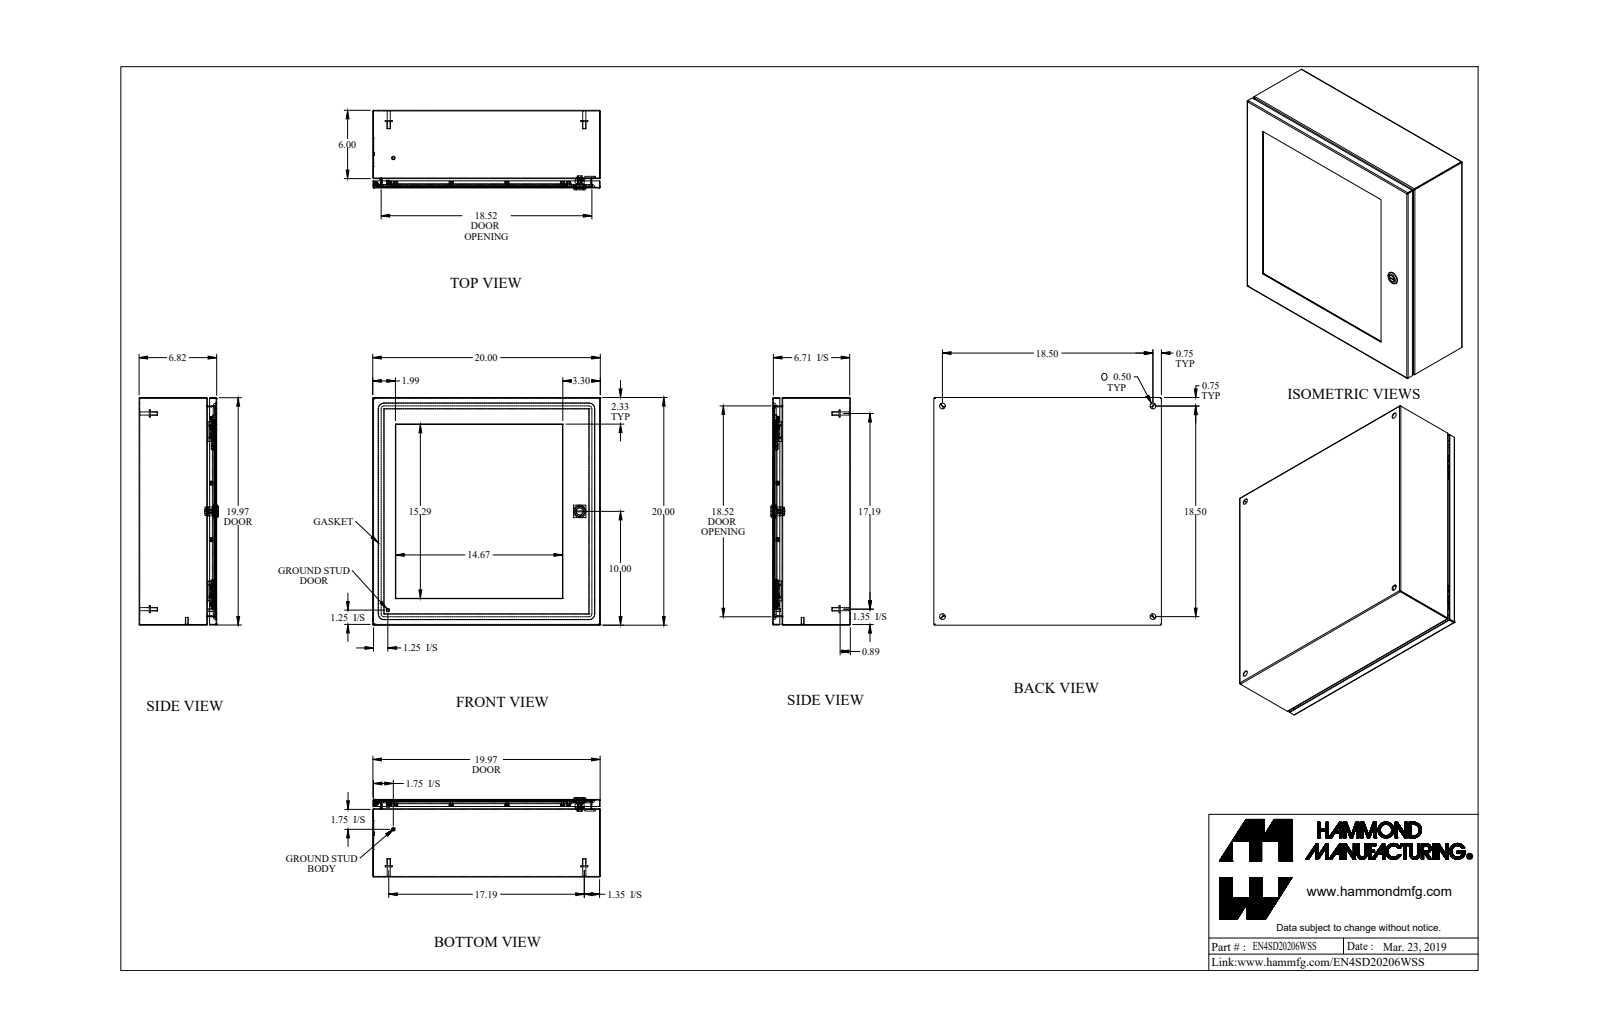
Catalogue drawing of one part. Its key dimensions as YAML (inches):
part_name: "EN4SD20206WSS_Default"
step_written_by: "SolidWorks 2019 (CONFIG_CONTROL_DESIGN)"
units: inches
bodies: {solids: 63, faces: 1287, planar: 646, cylindrical: 387, other: 254}
overall_size: [20, 20, 6.982]
volume: 142.9
surface_area: 3303
round_holes:
  - {diameter: 0.13, count: 16}
  - {diameter: 0.25, count: 16}
  - {diameter: 0.5, count: 5}
  - {diameter: 0.172, count: 1}
  - {diameter: 0.197, count: 1}
  - {diameter: 0.24, count: 1}
  - {diameter: 0.242, count: 1}
  - {diameter: 0.387, count: 1}
  - {diameter: 0.63, count: 1}
  - {diameter: 0.768, count: 1}
round_bosses_or_shafts:
  - {diameter: 0.226, count: 17}
  - {diameter: 0.368, count: 16}
  - {diameter: 0.164, count: 16}
  - {diameter: 0.313, count: 6}
  - {diameter: 0.625, count: 4}
  - {diameter: 0.275, count: 4}
  - {diameter: 0.25, count: 2}
  - {diameter: 1.1, count: 1}
partial_cylinders:
  - {radius: 0.029, count: 21}
  - {radius: 0.086, count: 21}
  - {radius: 0.188, count: 12}
  - {radius: 0.125, count: 10}
  - {radius: 0.006, count: 4}
  - {radius: 0.016, count: 4}
  - {radius: 0.062, count: 4}
  - {radius: 0.088, count: 4}
face_to_face_distances: [0.057, 6.765, 19.943, 6.708, 0.25, 6.458, 6.515, 19.886, 20, 0.307]
hole_center_spacings: [9.78, 16.333, 4.889, 4.89, 4.89, 4.891, 10.324, 16.471]
